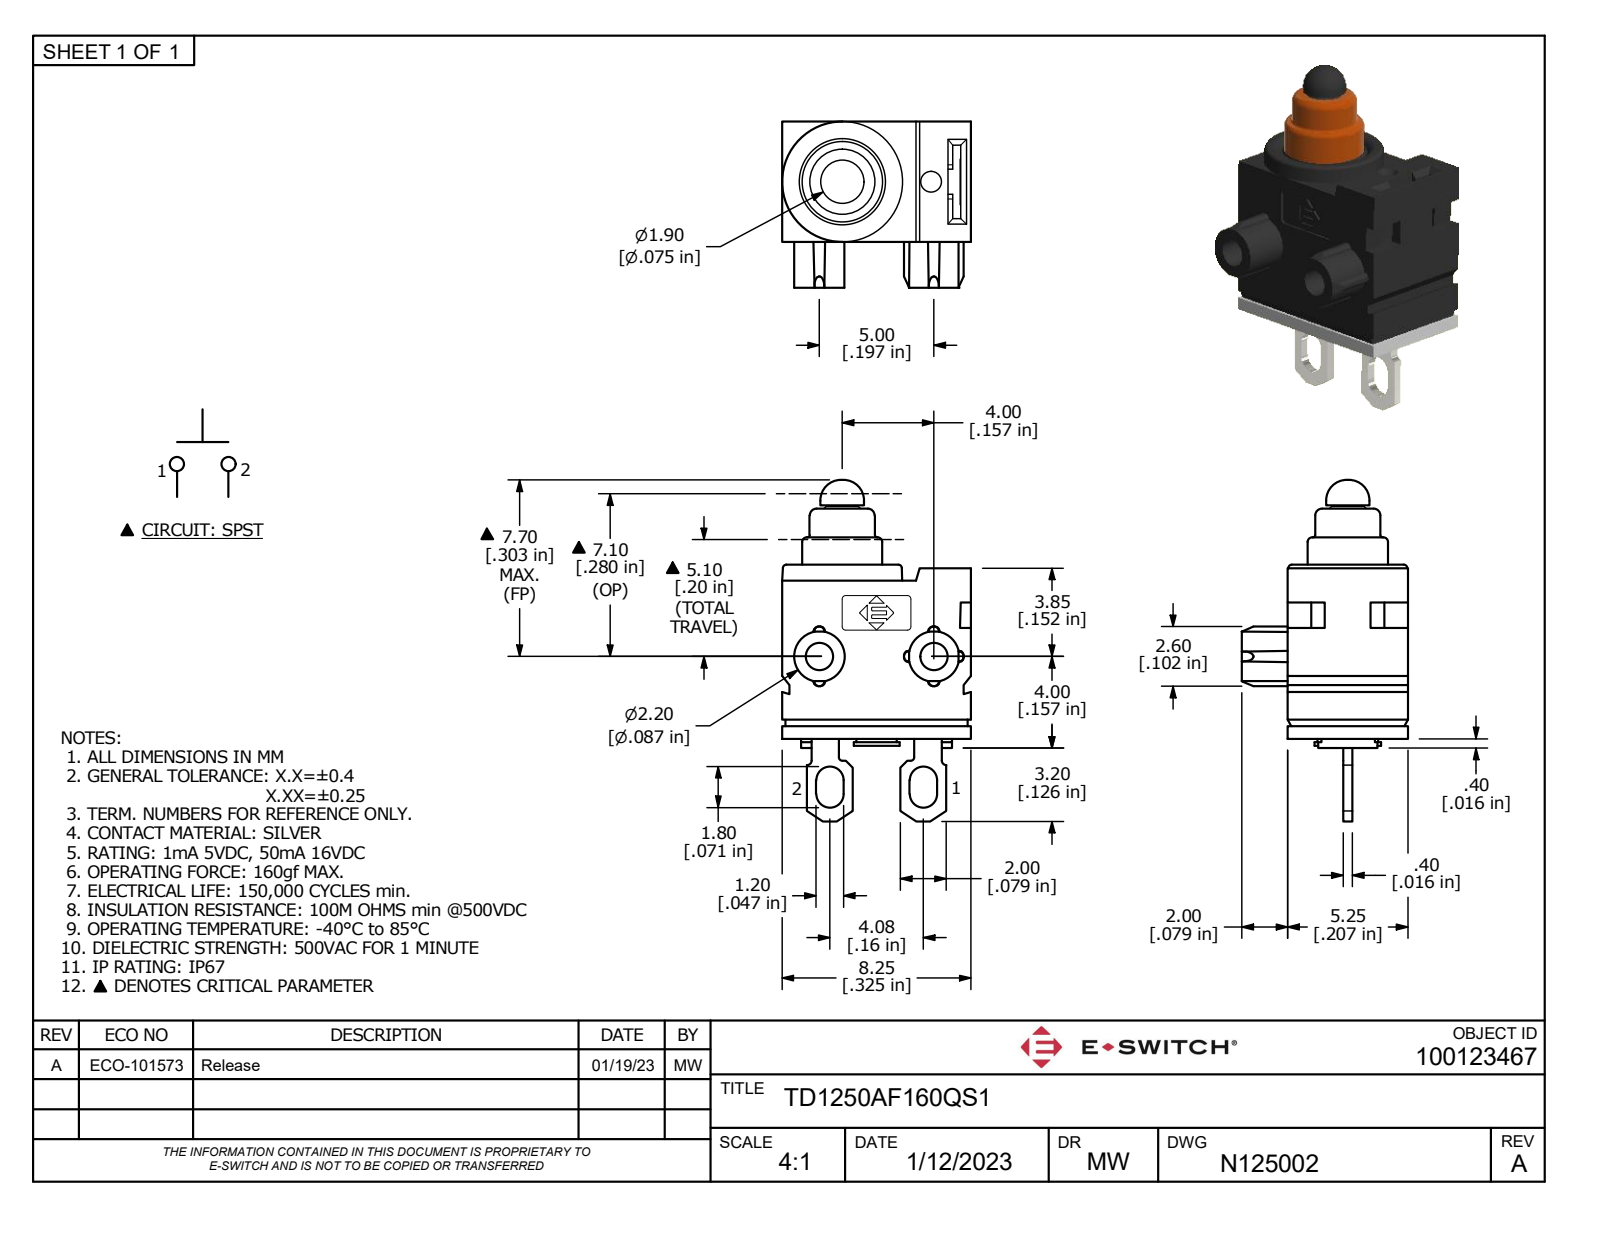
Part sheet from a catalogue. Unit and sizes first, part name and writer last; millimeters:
Units: millimetres
Overall size (bounding box): 14.9 × 8.25 × 7.25
Round holes (diameter × count): ⌀1.2 ×2, ⌀4.65 ×1
Round bosses / shafts (diameter × count): ⌀4.5 ×1, ⌀3.5 ×1, ⌀2.85 ×1, ⌀2.2 ×1, ⌀1.9 ×1, ⌀1.2 ×1
Partial cylindrical surfaces — rounded edges, fillets, slot ends (radius × count): R0.2 ×14, R0.15 ×8, R0.6 ×4, R0.1 ×3, R1.1 ×1
Main face-to-face distances: 5.24, 8.24, 0.55, 2.42, 2.82, 6.9, 7.45, 0.4, 7.24, 7.75
Hole centre spacings: 5
Volume: 350 mm³ · Surface area: 459 mm²
Bodies: 1 solid, 266 faces (203 planar, 51 cylindrical, 12 other)
Part name (STEP PRODUCT): TD1250AF160QS1
STEP written by: Autodesk Inventor 2022 (AUTOMOTIVE_DESIGN)
